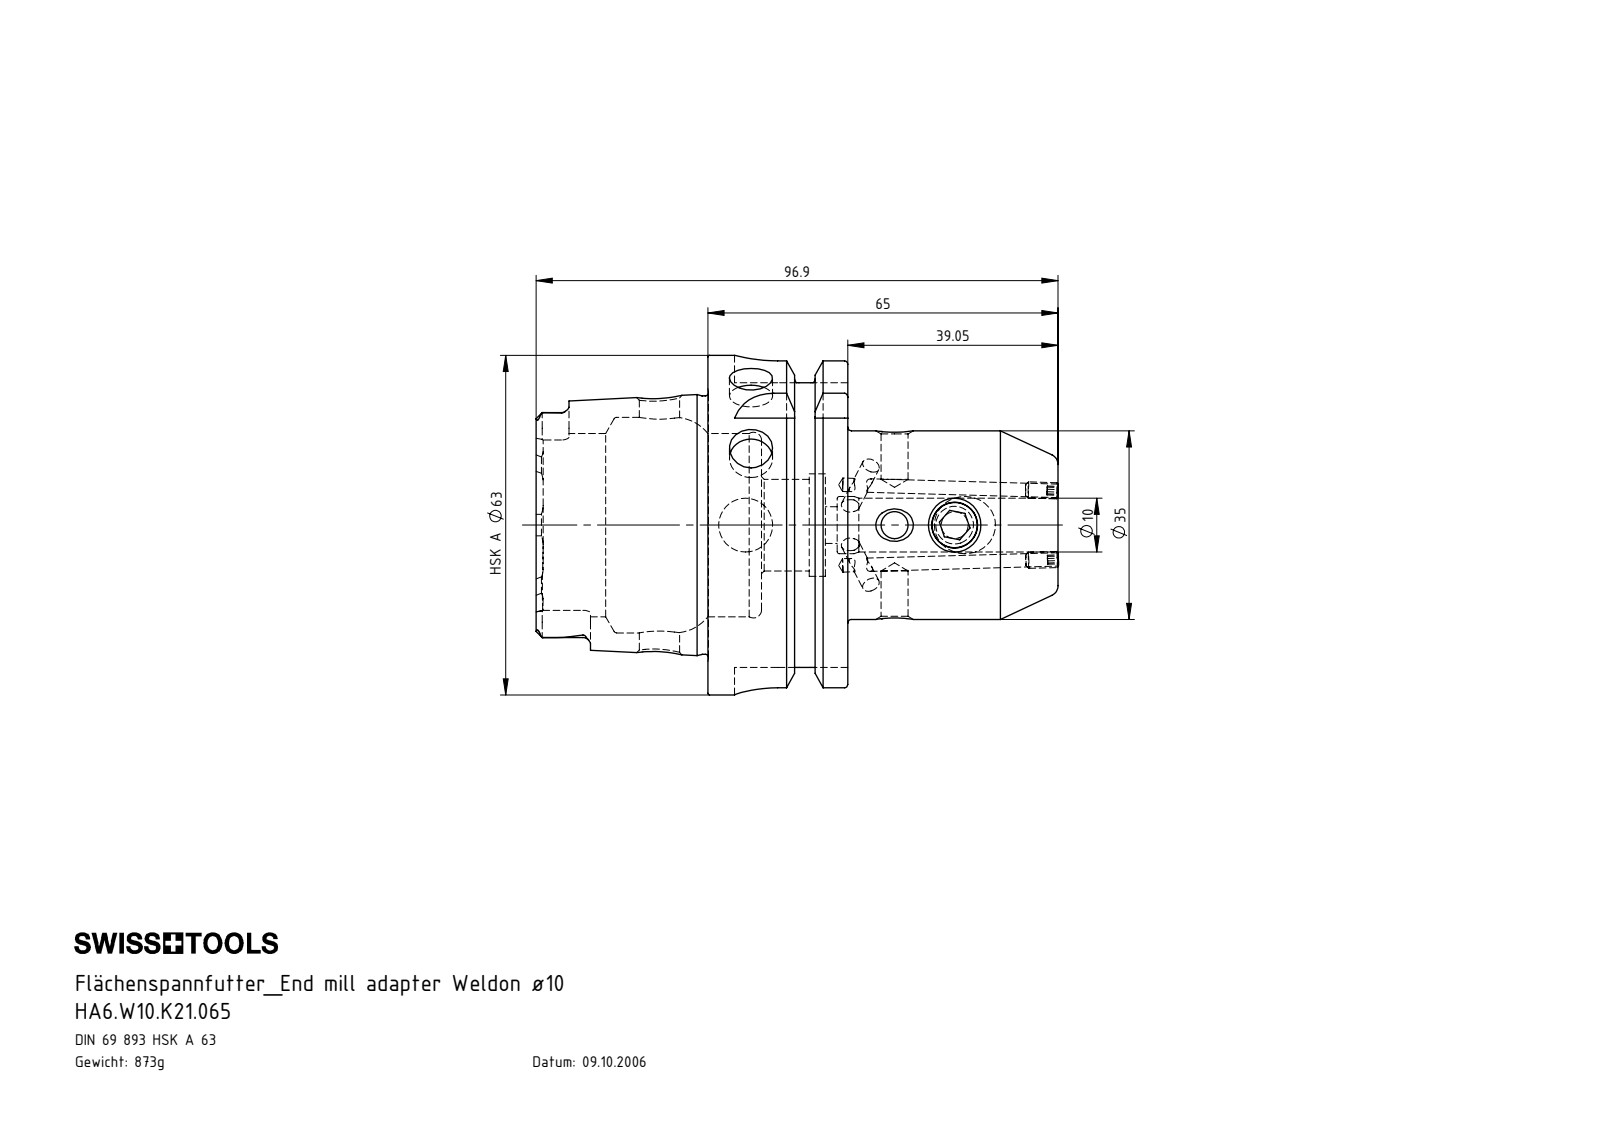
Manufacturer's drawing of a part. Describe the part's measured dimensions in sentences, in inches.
The part is named "HA6.W10.K21.065; ERU-CJ2.001.006; W10-ER1.001.012; HA6-W10.K21.065_C_Fertigbearbeitung". Its 3-D file was written by "SolidWorks 2012 (CONFIG_CONTROL_DESIGN)". It is 4 solids with 282 faces: 78 planar, 81 cylindrical and 123 other. Overall it measures 3.818 by 2.48 by 2.48 inches. Its volume is 6.788 cubic inches and its surface area 46.12 square inches. Round holes: 2 of diameter 0.098, 2 of diameter 0.13, 2 of diameter 0.197, 2 of diameter 0.315, 2 of diameter 0.394, 1 of diameter 0.268, 1 of diameter 0.295, 1 of diameter 0.335, 1 of diameter 0.417, 1 of diameter 0.669, 1 of diameter 0.748, 1 of diameter 1.339. Round bosses or shafts: 2 of diameter 0.118, 1 of diameter 2.48, 1 of diameter 2.163, 1 of diameter 1.887, 1 of diameter 1.378, 1 of diameter 0.394. Partial cylindrical surfaces (rounded edges, fillets, slot ends): 6 of radius 0.055, 4 of radius 0.113, 4 of radius 0.315. The main face-to-face distances are 1.022, 0.63, 0.392, 1.256, 1.648, 2.278, 0.858, 2.079, 3.815, 2.559. The hole center spacings are 0.439, 1.089, 1.528, 1.719.
